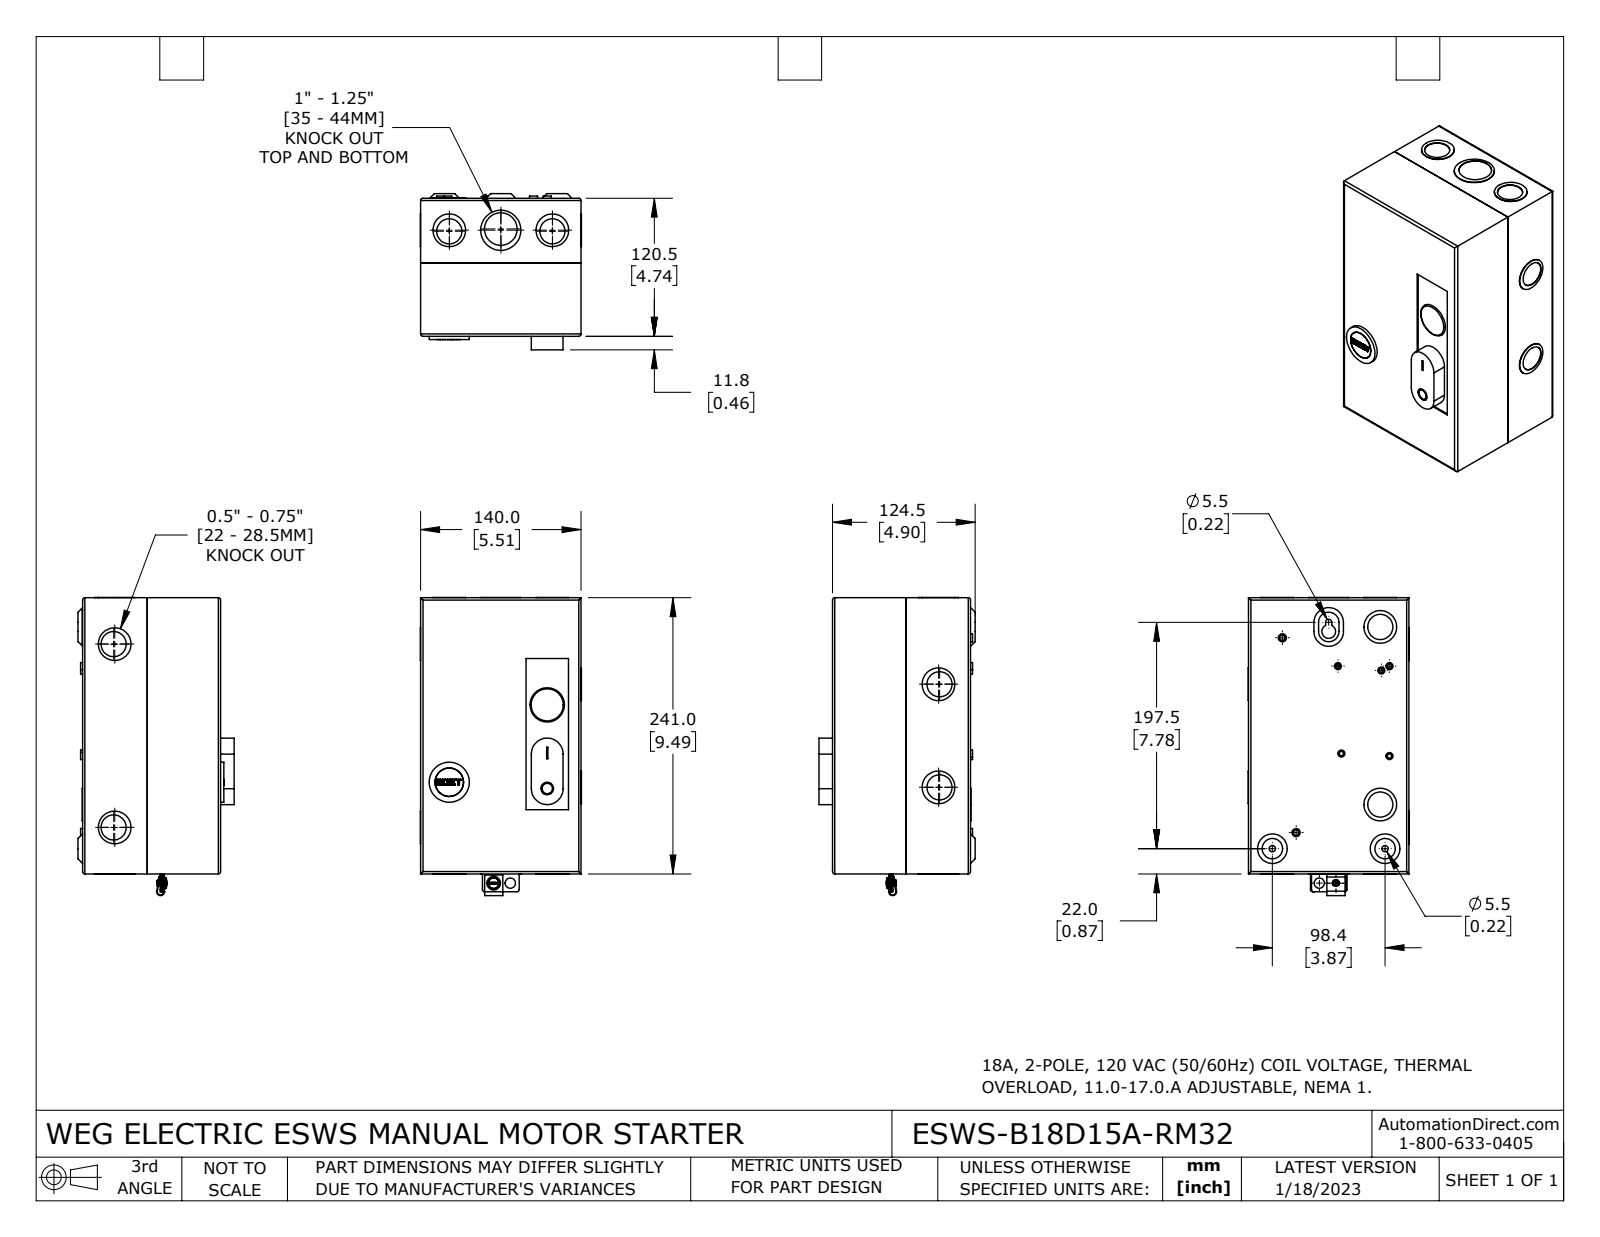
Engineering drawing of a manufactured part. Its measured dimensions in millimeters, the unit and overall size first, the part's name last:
Units: millimetres
Overall size (bounding box): 260.3 × 140.6 × 136.3
Round holes (diameter × count): ⌀3.7 ×5, ⌀21.9 ×4, ⌀4.6 ×2, ⌀5.5 ×2, ⌀9 ×2, ⌀21.9 ×2, ⌀22 ×2, ⌀22.5 ×2, ⌀6.5 ×1, ⌀7.7 ×1, ⌀11 ×1, ⌀11.9 ×1
Round bosses / shafts (diameter × count): ⌀28.5 ×6, ⌀6.1 ×5, ⌀28.5 ×2, ⌀7.1 ×2, ⌀35.1 ×1, ⌀35 ×1, ⌀30.3 ×1, ⌀29.2 ×1
Partial cylindrical surfaces — rounded edges, fillets, slot ends (radius × count): R0.1 ×34, R2 ×13, R0.8 ×4, R2.7 ×3, R1.5 ×2, R1.9 ×2, R3.1 ×2, R3.5 ×2
Main face-to-face distances: 1.2, 119.3, 138.8, 118.1, 239.8, 120.5, 137.6, 140, 1.8, 1.6
Hole centre spacings: 14.5, 35, 45, 86, 90, 125, 152.3, 190.1
Volume: 266 000 mm³ · Surface area: 377 500 mm²
Bodies: 7 solids, 435 faces (168 planar, 230 cylindrical, 37 other)
Part name (STEP PRODUCT): ESWS-B18D15A-RM32
STEP written by: SolidWorks 2021 (CONFIG_CONTROL_DESIGN)
